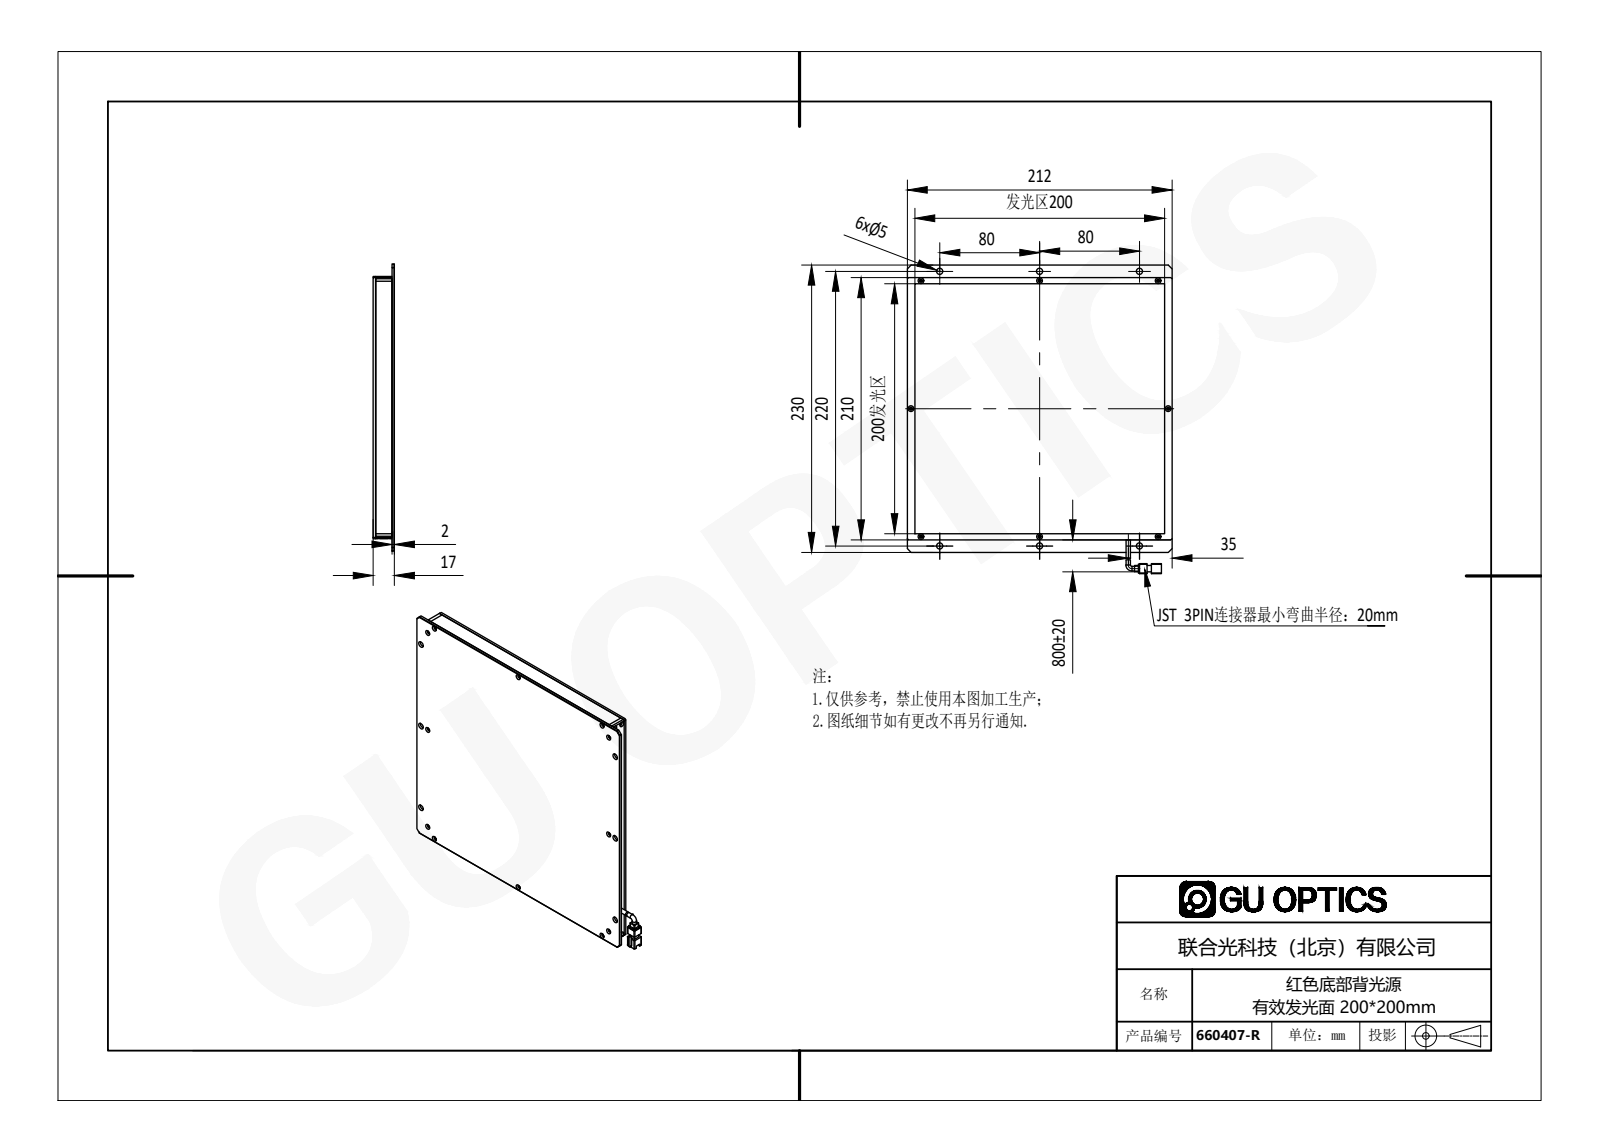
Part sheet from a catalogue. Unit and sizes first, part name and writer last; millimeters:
Units: millimetres
Overall size (bounding box): 247 × 212 × 20.3
Round holes (diameter × count): ⌀1.6 ×16, ⌀2.4 ×16, ⌀5 ×6
Round bosses / shafts (diameter × count): ⌀3.5 ×2
Partial cylindrical surfaces — rounded edges, fillets, slot ends (radius × count): R0.5 ×8, R1 ×4, R2 ×2, R1.6 ×1
Main face-to-face distances: 15, 2, 13, 3, 16, 18, 6, 206, 200, 5
Hole centre spacings: 95, 206, 10.97, 16.77, 27.46, 80, 80.35, 95.3
Volume: 283 962 mm³ · Surface area: 223 998 mm²
Bodies: 8 solids, 522 faces (199 planar, 149 cylindrical, 174 other)
Part name (STEP PRODUCT): 660407-R
STEP written by: SolidWorks 2016 (AUTOMOTIVE_DESIGN)
